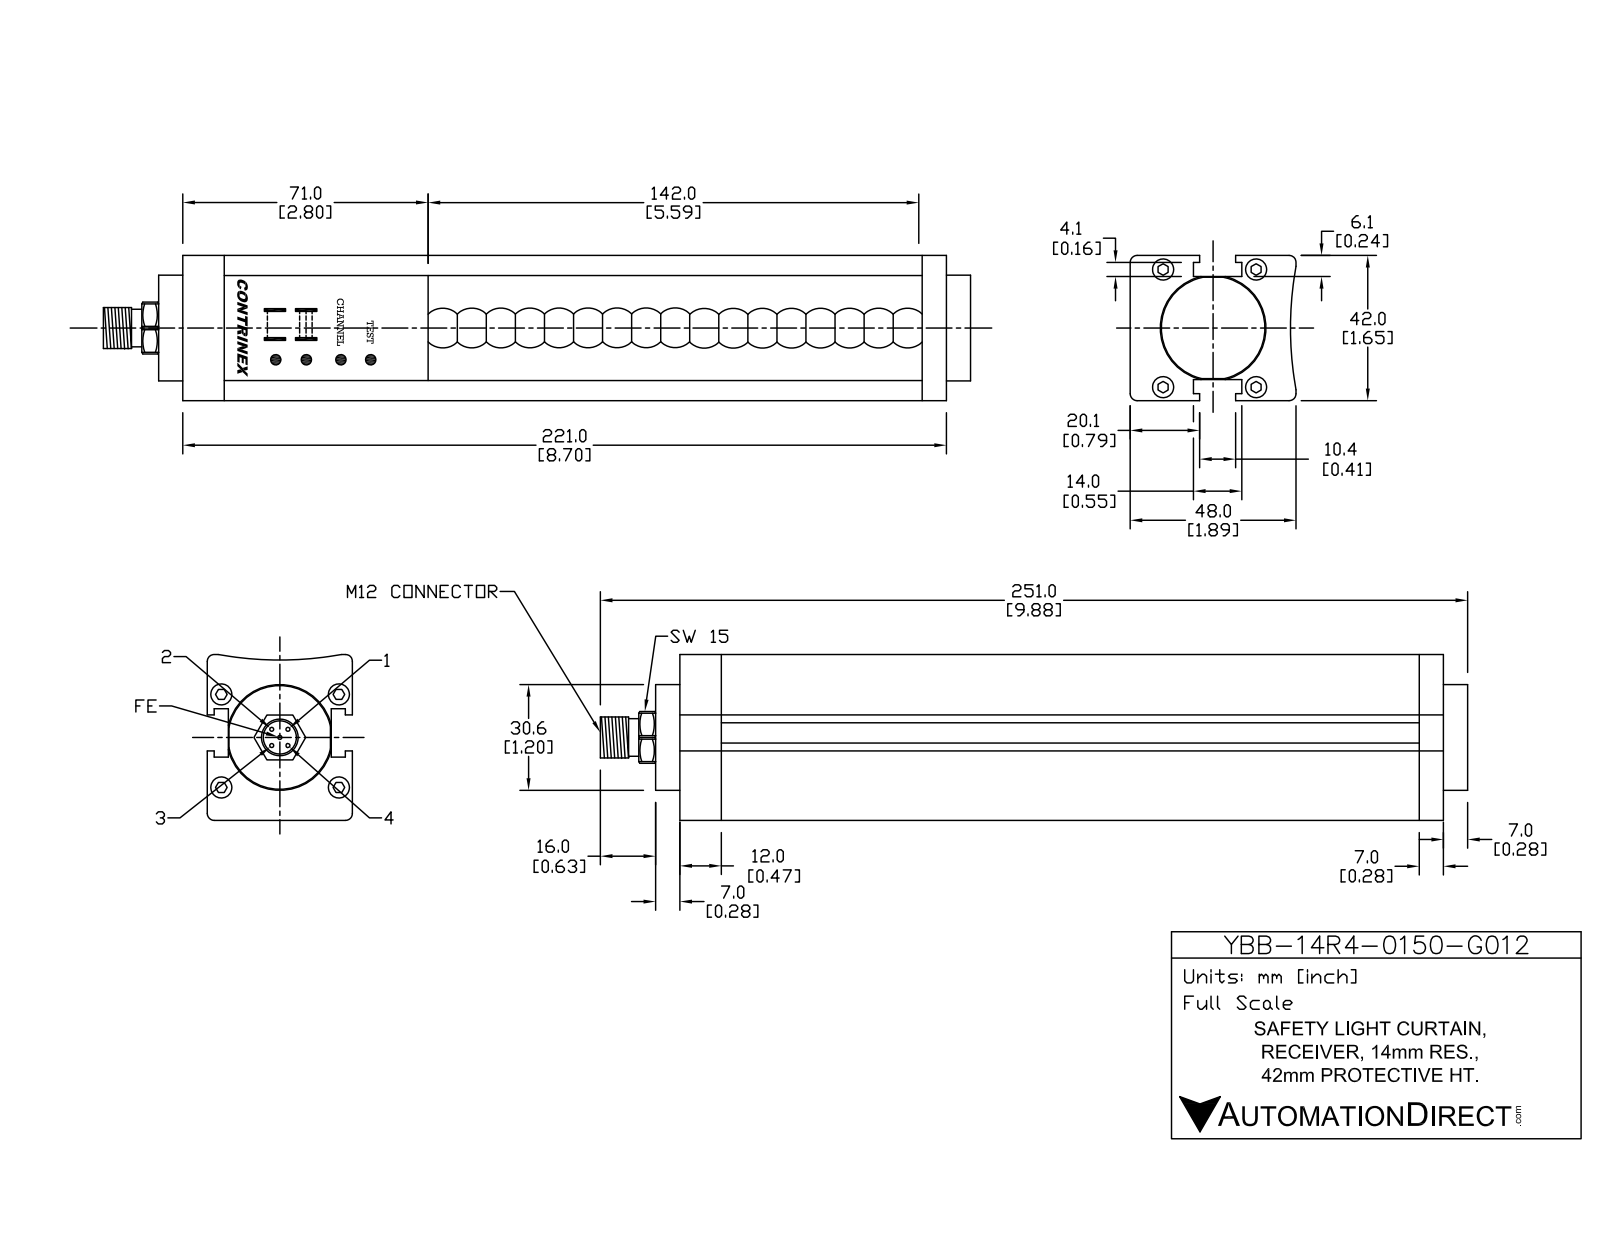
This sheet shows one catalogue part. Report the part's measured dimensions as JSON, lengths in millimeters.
{"part_name": "YBB-14R4-0150-G012", "step_written_by": "SolidWorks 2016 (AUTOMOTIVE_DESIGN)", "units": "millimeters", "bodies": {"solids": 19, "faces": 440, "planar": 208, "cylindrical": 168, "other": 64}, "overall_size": [251, 48, 42], "volume_mm3": 406321, "surface_area_mm2": 64999, "round_holes": [[6, 4], [8.5, 1], [32, 1]], "round_bosses_or_shafts": [[1, 5], [5.5, 4], [30.6, 1], [12, 1], [10.5, 1]], "partial_cylinders_radius": [[1, 48], [0.5, 4], [0.55, 2], [8.2, 1], [100, 1]], "face_to_face_distances": [6.3, 35.7, 42, 201, 29.4, 8, 12, 213, 221, 209], "hole_center_spacings": [21.04, 22.34, 26.9, 34, 43.35]}
